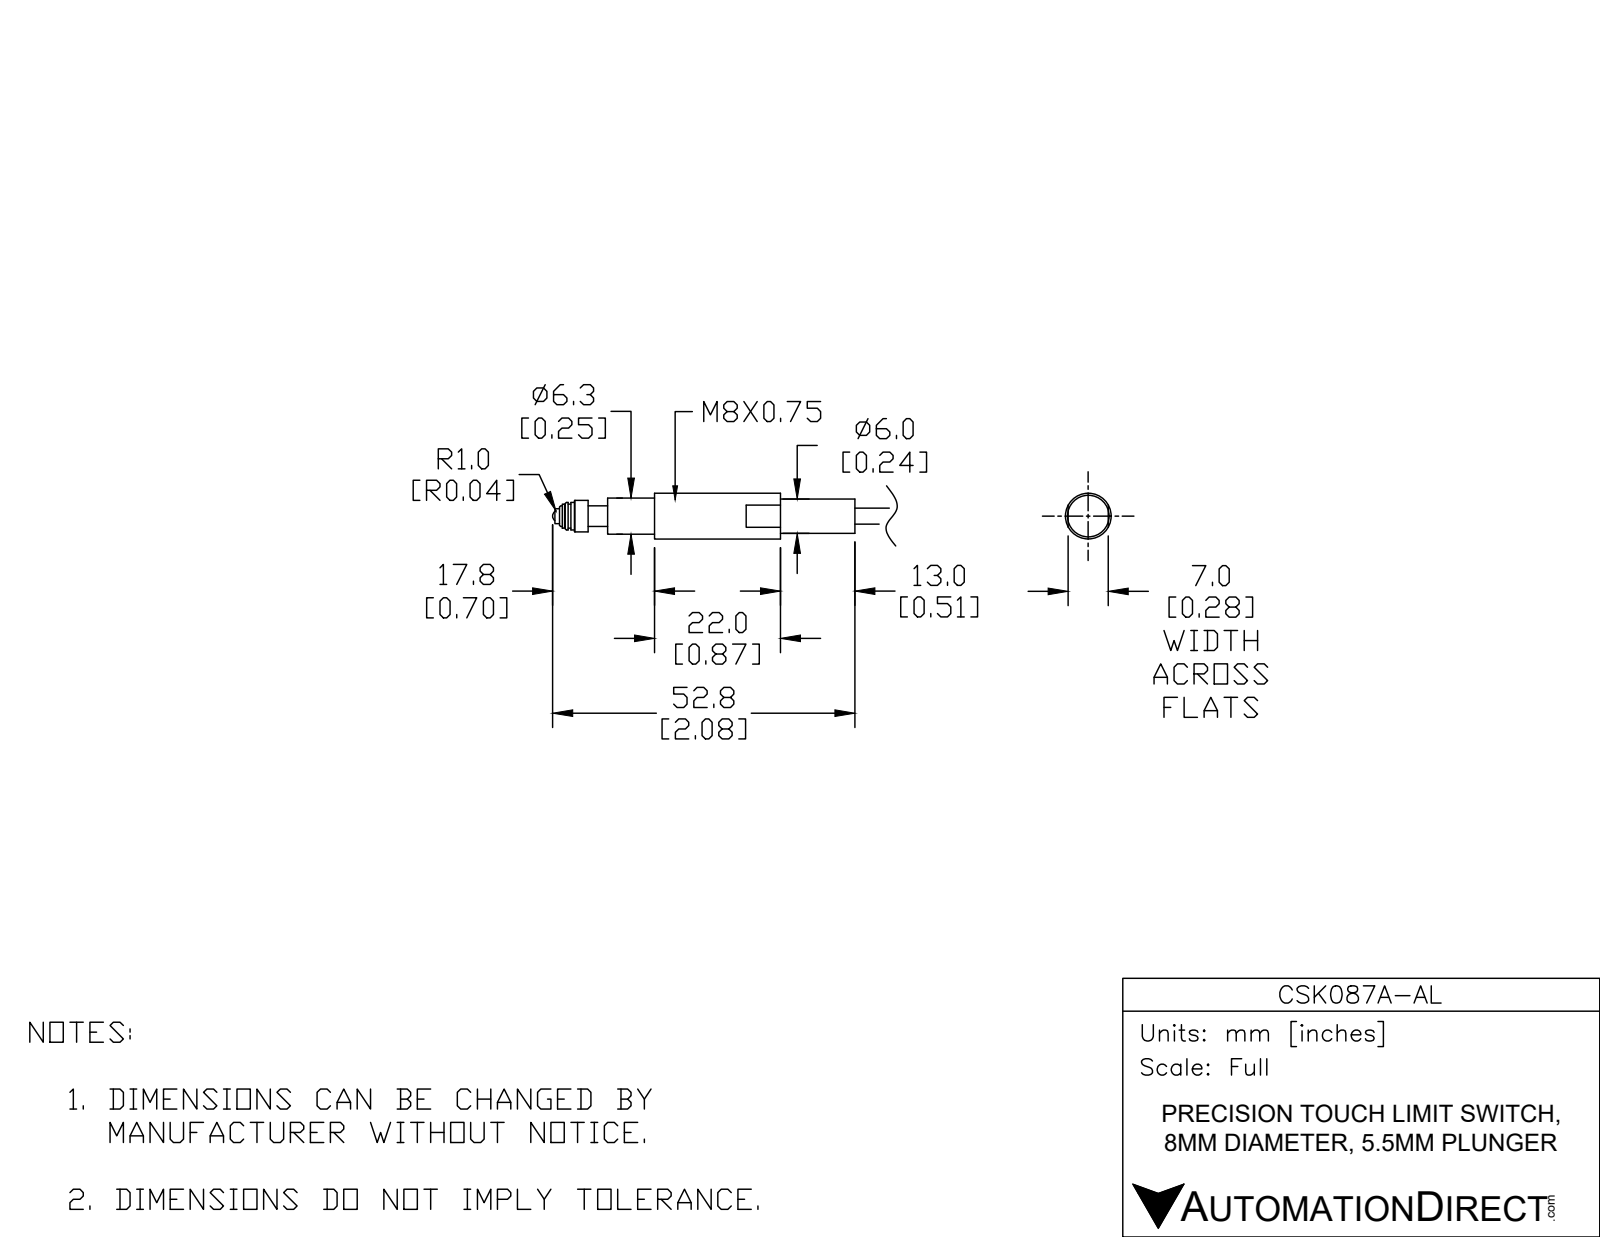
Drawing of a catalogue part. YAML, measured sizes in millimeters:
part_name: "CSP087A-AL"
step_written_by: "SolidWorks 2017 (AUTOMOTIVE_DESIGN)"
units: millimeters
bodies: {solids: 1, faces: 161, planar: 18, cylindrical: 84, other: 59}
overall_size: [58.8, 8, 8]
volume: 1770
surface_area: 1560
round_bosses_or_shafts:
  - {diameter: 8, count: 1}
  - {diameter: 6.3, count: 1}
  - {diameter: 6, count: 1}
  - {diameter: 5.5, count: 1}
  - {diameter: 4.8, count: 1}
  - {diameter: 4.2, count: 1}
  - {diameter: 3.6, count: 1}
  - {diameter: 2.8, count: 1}
face_to_face_distances: [43.2, 3.4, 7, 0.5, 30.2, 13, 33.6, 46.6, 11.6, 8.2]
